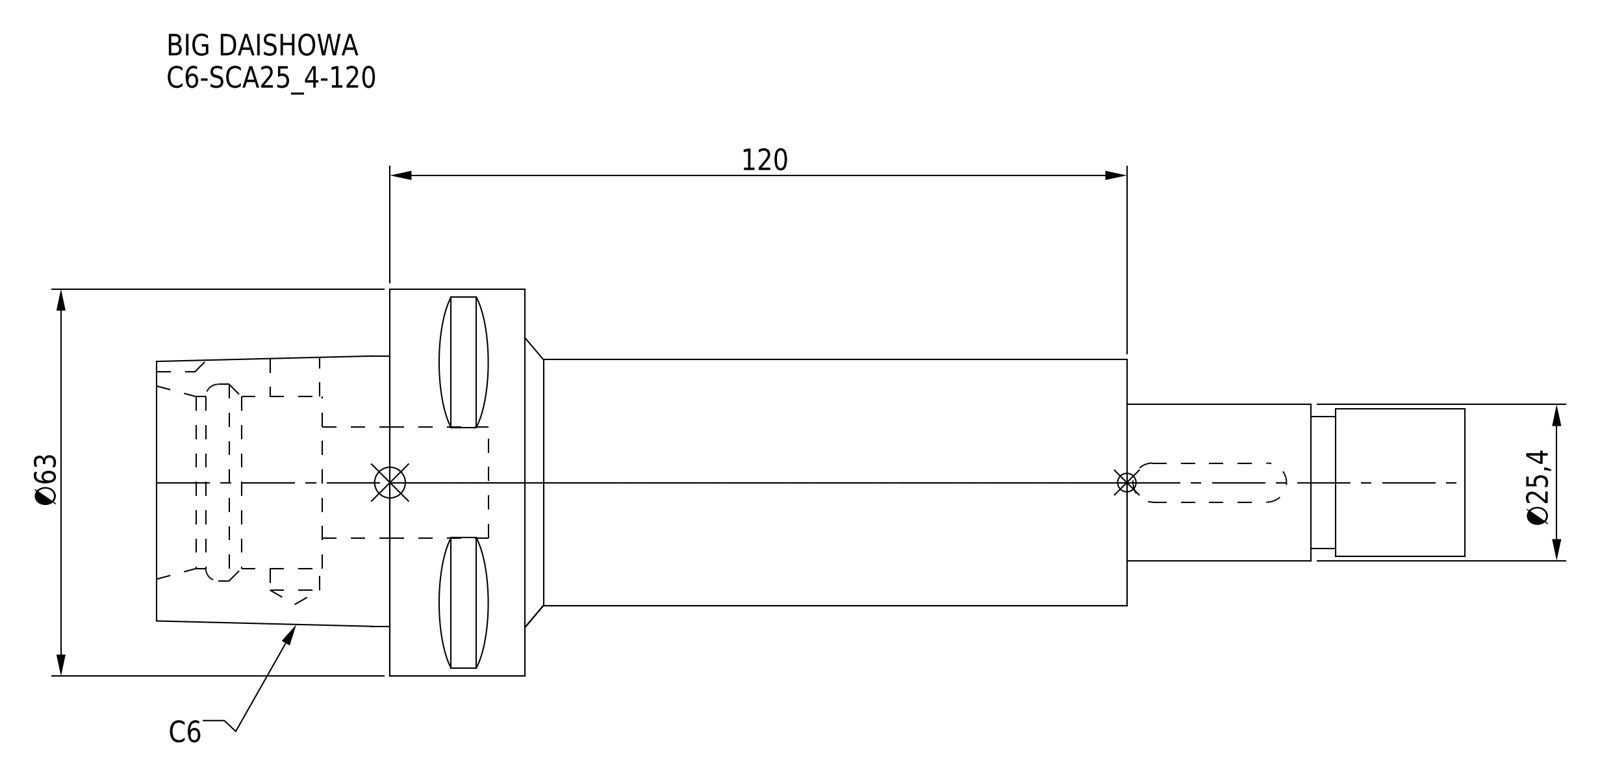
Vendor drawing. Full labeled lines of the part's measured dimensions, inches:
Part name (STEP PRODUCT): C6-SCA25_4-120
STEP written by: CREO PARAMETRIC BY PTC INC, 2016380 (AUTOMOTIVE_DESIGN)
Units: inches
Bodies: 1 solid, 71 faces (34 planar, 25 cylindrical, 12 other)
Overall size (bounding box): 8.386 × 2.48 × 2.48
Volume: 15.07 in³ · Surface area: 57.06 in²
Round holes (diameter × count): ⌀0.319 ×1, ⌀0.709 ×1, ⌀1.102 ×1, ⌀1.26 ×1
Round bosses / shafts (diameter × count): ⌀2.48 ×1, ⌀1.575 ×1, ⌀1 ×1, ⌀0.945 ×1, ⌀0.846 ×1
Partial cylindrical surfaces — rounded edges, fillets, slot ends (radius × count): R0.125 ×2, R0.197 ×1
Main face-to-face distances: 0.866, 3.858, 4.724, 1.063, 6.22, 2.362, 1.496, 2.165, 6.024, 6.89
